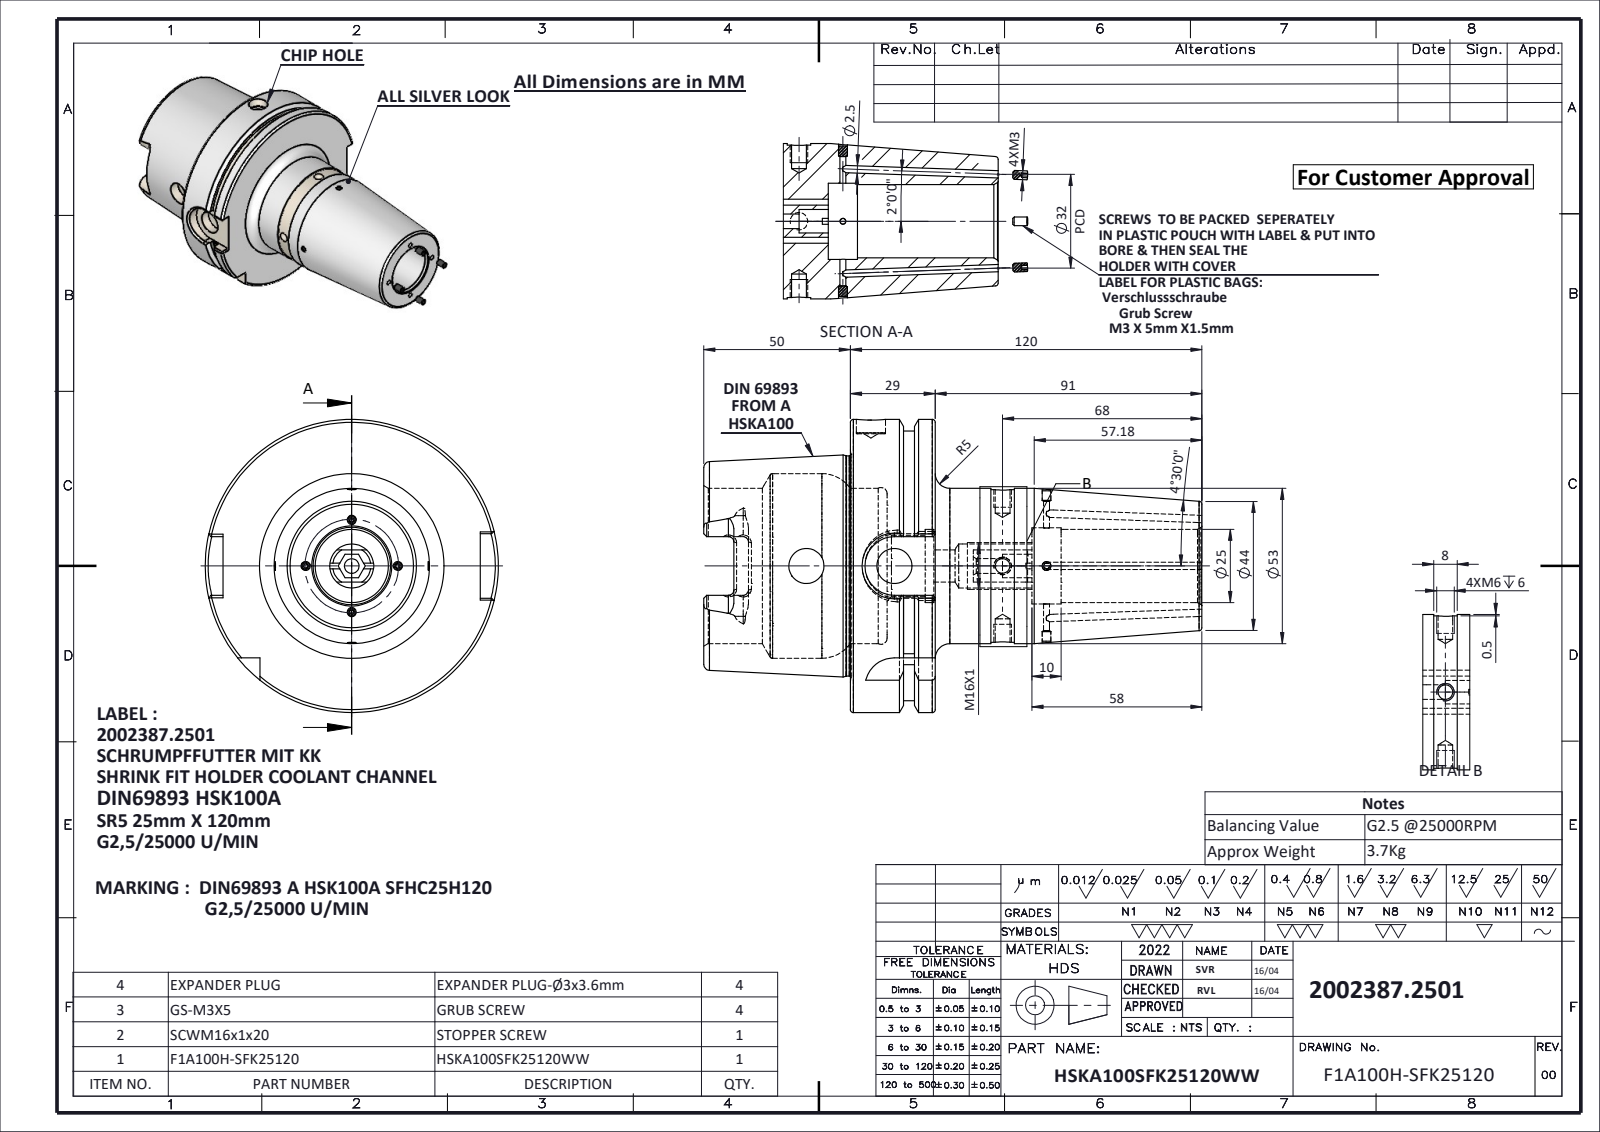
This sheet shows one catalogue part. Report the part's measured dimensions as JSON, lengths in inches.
{"part_name": "EXPANDER PLUG Ø3x3.6; HSKA100SFK25120WW; F1A100H-SFK25120; GS-M3X5 (+1 more)", "step_written_by": "SolidWorks 2024 (CONFIG_CONTROL_DESIGN)", "units": "inches", "bodies": {"solids": 10, "faces": 389, "planar": 137, "cylindrical": 114, "other": 138}, "overall_size": [7.086, 3.937, 3.937], "volume_in3": 24.47, "surface_area_in2": 114.3, "round_holes": [[0.098, 4], [0.197, 3], [0.079, 2], [0.118, 2], [0.472, 2], [0.394, 1], [0.433, 1], [0.591, 1], [0.827, 1], [0.984, 1], [1.024, 1], [2.087, 1]], "round_bosses_or_shafts": [[0.118, 4], [3.937, 1], [3.622, 1], [2.959, 1], [2.047, 1]], "partial_cylinders_radius": [[0.071, 6], [0.192, 4], [0.394, 2], [0.315, 1], [0.433, 1]], "face_to_face_distances": [1.14, 0.648, 0.492, 1.969, 2.461, 3.108, 6.691, 4.722, 4.23, 3.583], "hole_center_spacings": [0.591, 1.181, 1.455, 1.77, 2.045, 2.36, 2.636, 3.226]}
